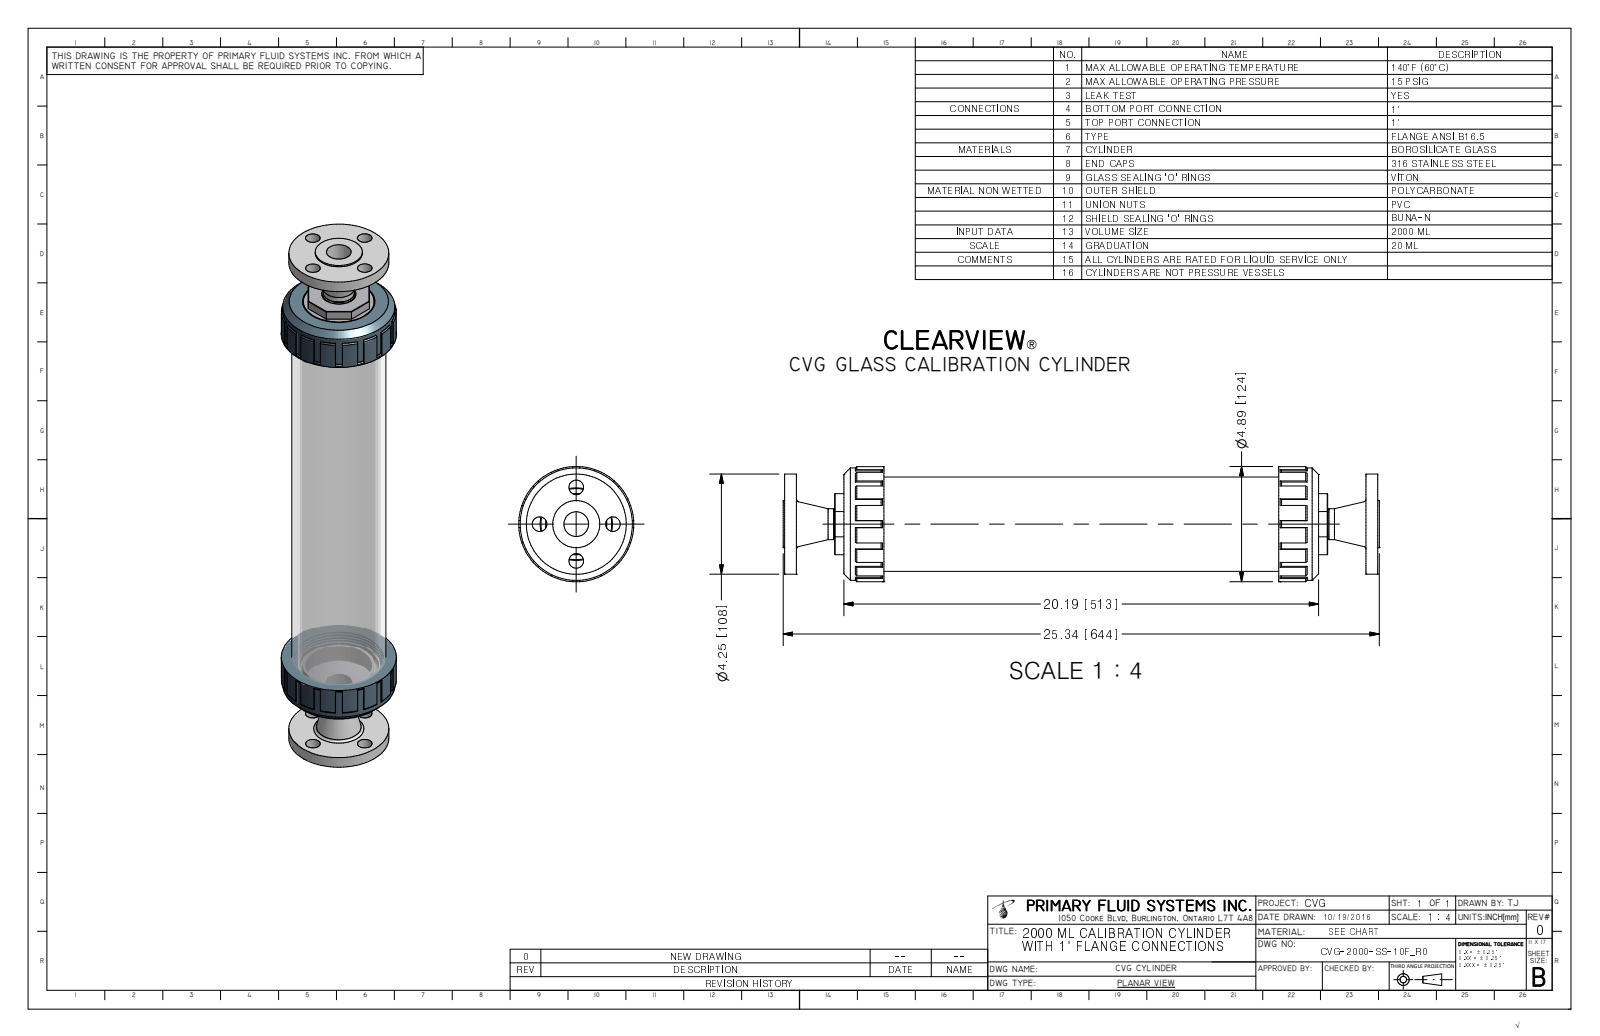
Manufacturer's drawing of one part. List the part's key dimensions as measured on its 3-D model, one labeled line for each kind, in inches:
Part name (STEP PRODUCT): CVG-2000-SS-10F_R0; CVG-3-2000-METAL-S-10_R1; CVG-6-2000; CVG-1-2000-A_R0 (+2 more)
STEP written by: Autodesk Inventor 2009 (AUTOMOTIVE_DESIGN)
Units: inches
Bodies: 8 solids, 342 faces (108 planar, 82 cylindrical, 152 other)
Overall size (bounding box): 25.34 × 4.89 × 4.89
Volume: 118.1 in³ · Surface area: 1 187 in²
Round holes (diameter × count): ⌀0.62 ×4, ⌀1.049 ×1, ⌀1.157 ×1, ⌀1.36 ×1, ⌀2.825 ×1, ⌀3.075 ×1, ⌀3.15 ×1, ⌀3.4 ×1, ⌀3.58 ×1, ⌀3.819 ×1, ⌀3.945 ×1, ⌀3.945 ×1
Round bosses / shafts (diameter × count): ⌀4.89 ×1, ⌀4.77 ×1, ⌀4.25 ×1, ⌀4 ×1, ⌀3.74 ×1, ⌀3.55 ×1, ⌀3.412 ×1, ⌀3.346 ×1
Main face-to-face distances: 0.5, 24.715, 2.513, 22.702, 2.013, 22.202, 4.213, 21.002, 3.713, 20.502
Hole centre spacings: 1.56, 2.206, 3.12
